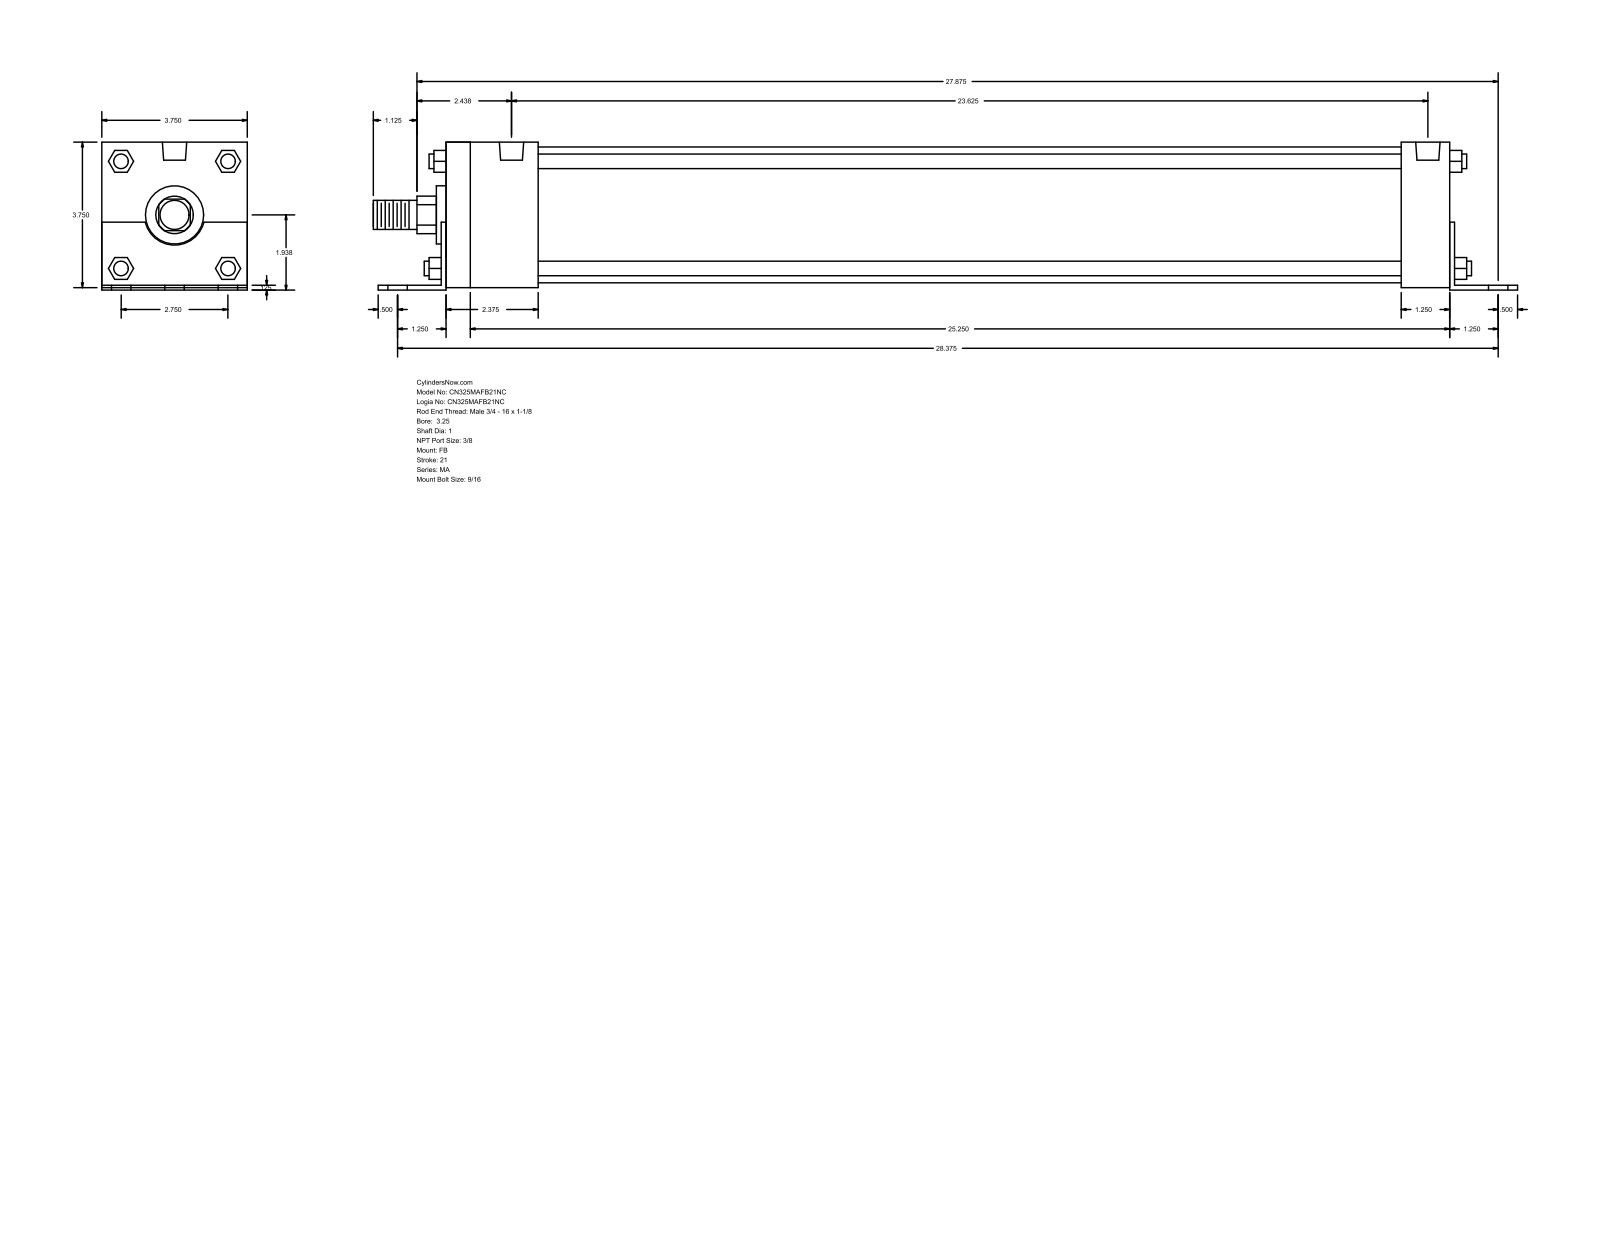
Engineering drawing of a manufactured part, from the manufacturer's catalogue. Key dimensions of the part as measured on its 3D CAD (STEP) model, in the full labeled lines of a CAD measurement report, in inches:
Part name (STEP PRODUCT): MA_FB__0325_1
STEP written by: GSSL Pune (CONFIG_CONTROL_DESIGN)
Units: inches
Bodies: 0 solids, 140 faces (105 planar, 35 cylindrical, 0 other)
Overall size (bounding box): 29.5 × 3.813 × 3.75
Round holes (diameter × count): ⌀0.563 ×6, ⌀0.437 ×4, ⌀0.627 ×2
Round bosses / shafts (diameter × count): ⌀0.375 ×4, ⌀3.5 ×1, ⌀1.5 ×1, ⌀1 ×1, ⌀0.75 ×1
Partial cylindrical surfaces — rounded edges, fillets, slot ends (radius × count): R0.484 ×1, R0.78 ×1
Main face-to-face distances: 3.75, 0.125, 0.063, 3.812, 0.062, 3.687, 0.125, 25.875, 26.125, 26
Hole centre spacings: 1.375, 28.408, 28.375, 0.187, 2.275, 2.427, 2.75, 3.243
